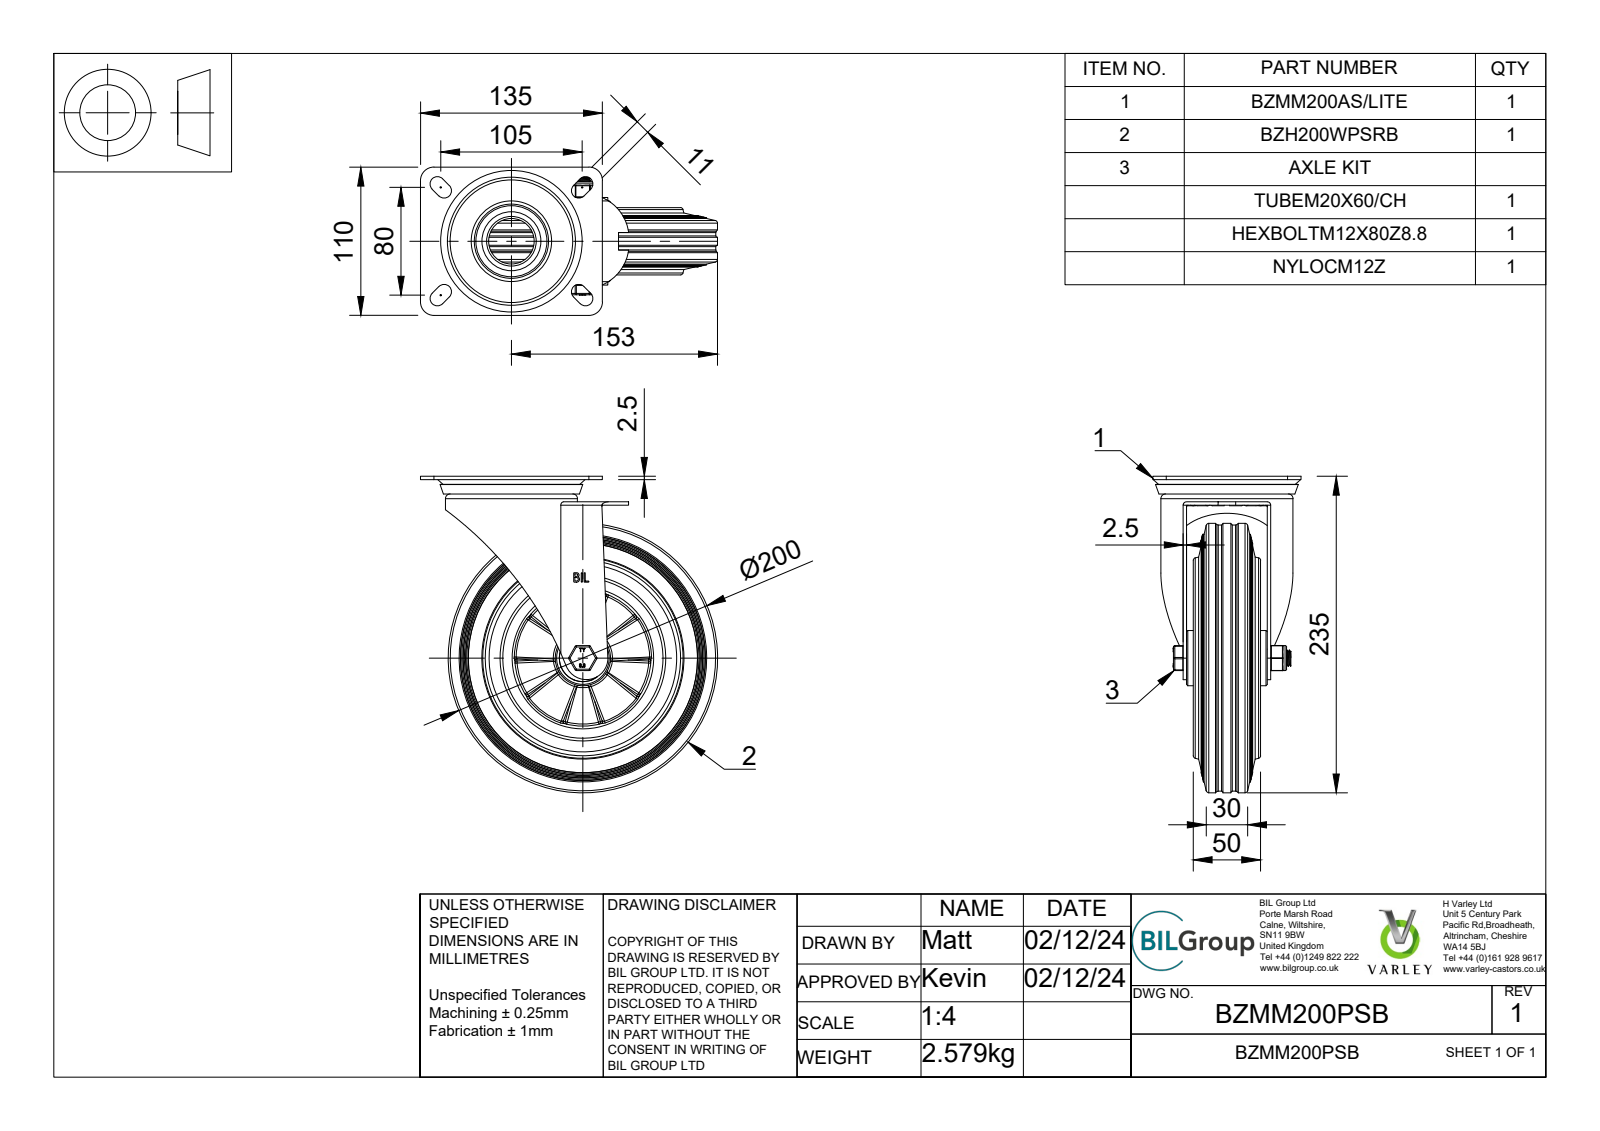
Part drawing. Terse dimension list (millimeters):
name: BZMM200PSB v3; BZMM200AS/LITE - 2 v1; ZINC PLATED, PRESSED STEEL TOP PLATE; ZINC PLATED, PRESSED STEEL TOP PLATE Geometry (+7 more)
written by: Autodesk Translation Framework v13.20.0.188 (AP242_MANAGED_MODEL_BASED_3D_ENGINEERING_MIM_LF)
unit: mm
bodies: 59 solids, 878 faces (255 planar, 164 cylindrical, 459 other)
size: 235 × 220.5 × 110
volume: 1 226 000 mm³; area: 311 683 mm²
holes: 1× ⌀12, 1× ⌀12.2, 1× ⌀12.5, 1× ⌀14, 1× ⌀20, 1× ⌀33.75, 1× ⌀35, 1× ⌀55, 1× ⌀91, 1× ⌀101, 1× ⌀118
bosses: 8× ⌀7.5, 1× ⌀200, 1× ⌀197.5, 1× ⌀123, 1× ⌀98, 1× ⌀78, 1× ⌀50, 1× ⌀41
rounds: 18× R0.5, 12× R1, 8× R5.5, 4× R1.25, 4× R10, 2× R2.5, 2× R32.86, 1× R13.5
face distances: 2.5, 9, 6.5, 53.5, 62.5, 5, 60, 13.5, 11, 3
